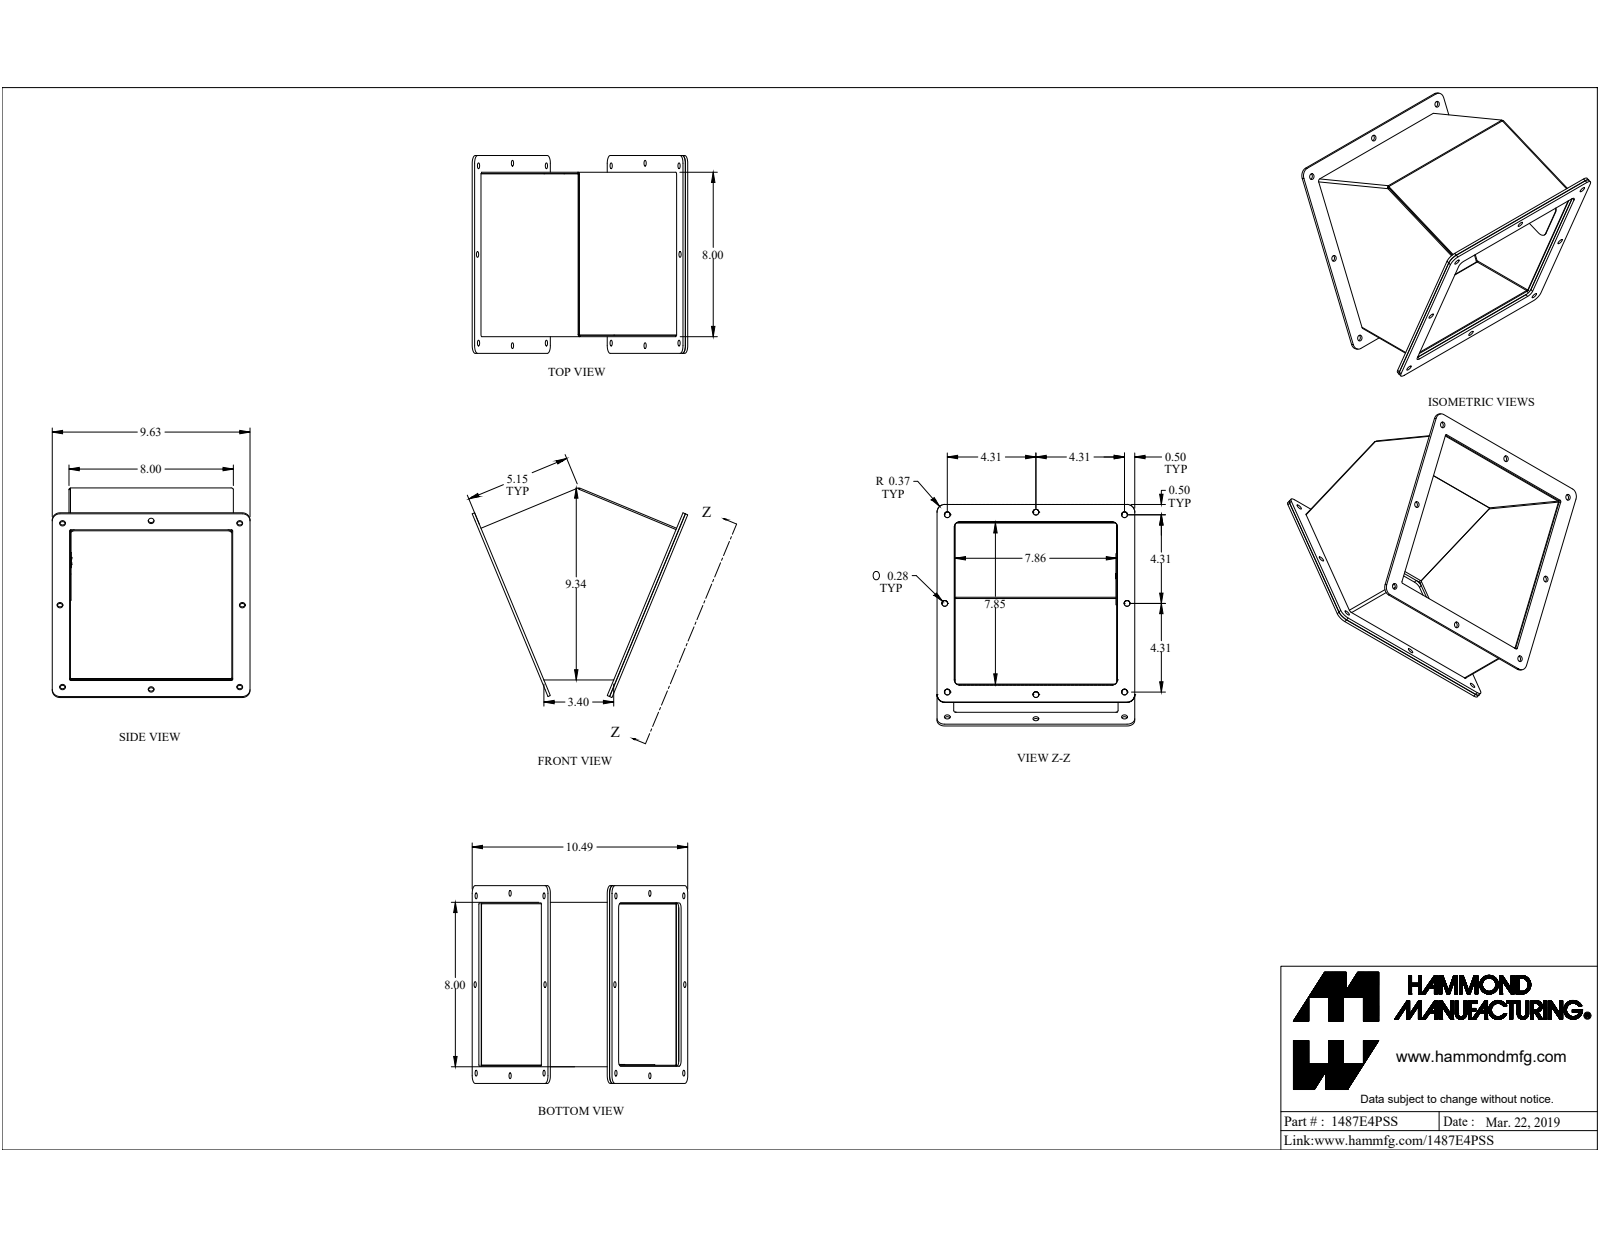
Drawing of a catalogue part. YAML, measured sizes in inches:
part_name: "1487E4PSS"
step_written_by: "SolidWorks 2019 (CONFIG_CONTROL_DESIGN)"
units: inches
bodies: {solids: 8, faces: 278, planar: 165, cylindrical: 82, other: 31}
overall_size: [10.573, 10.198, 9.625]
volume: 27.12
surface_area: 672.2
round_holes:
  - {diameter: 0.281, count: 24}
  - {diameter: 0.196, count: 1}
  - {diameter: 0.258, count: 1}
  - {diameter: 0.35, count: 1}
round_bosses_or_shafts:
  - {diameter: 0.5, count: 1}
  - {diameter: 0.25, count: 1}
partial_cylinders:
  - {radius: 0.375, count: 14}
  - {radius: 0.02, count: 6}
  - {radius: 0.036, count: 4}
  - {radius: 0.062, count: 4}
  - {radius: 0.063, count: 4}
  - {radius: 0.108, count: 4}
  - {radius: 0.25, count: 4}
face_to_face_distances: [0.072, 7.928, 0.125, 7.856, 8, 0.25, 0.125, 7.898, 7.826, 0.03]
hole_center_spacings: [4.315, 9.755, 8.625, 4.314, 6.276, 8.875, 9.753, 9.757]
